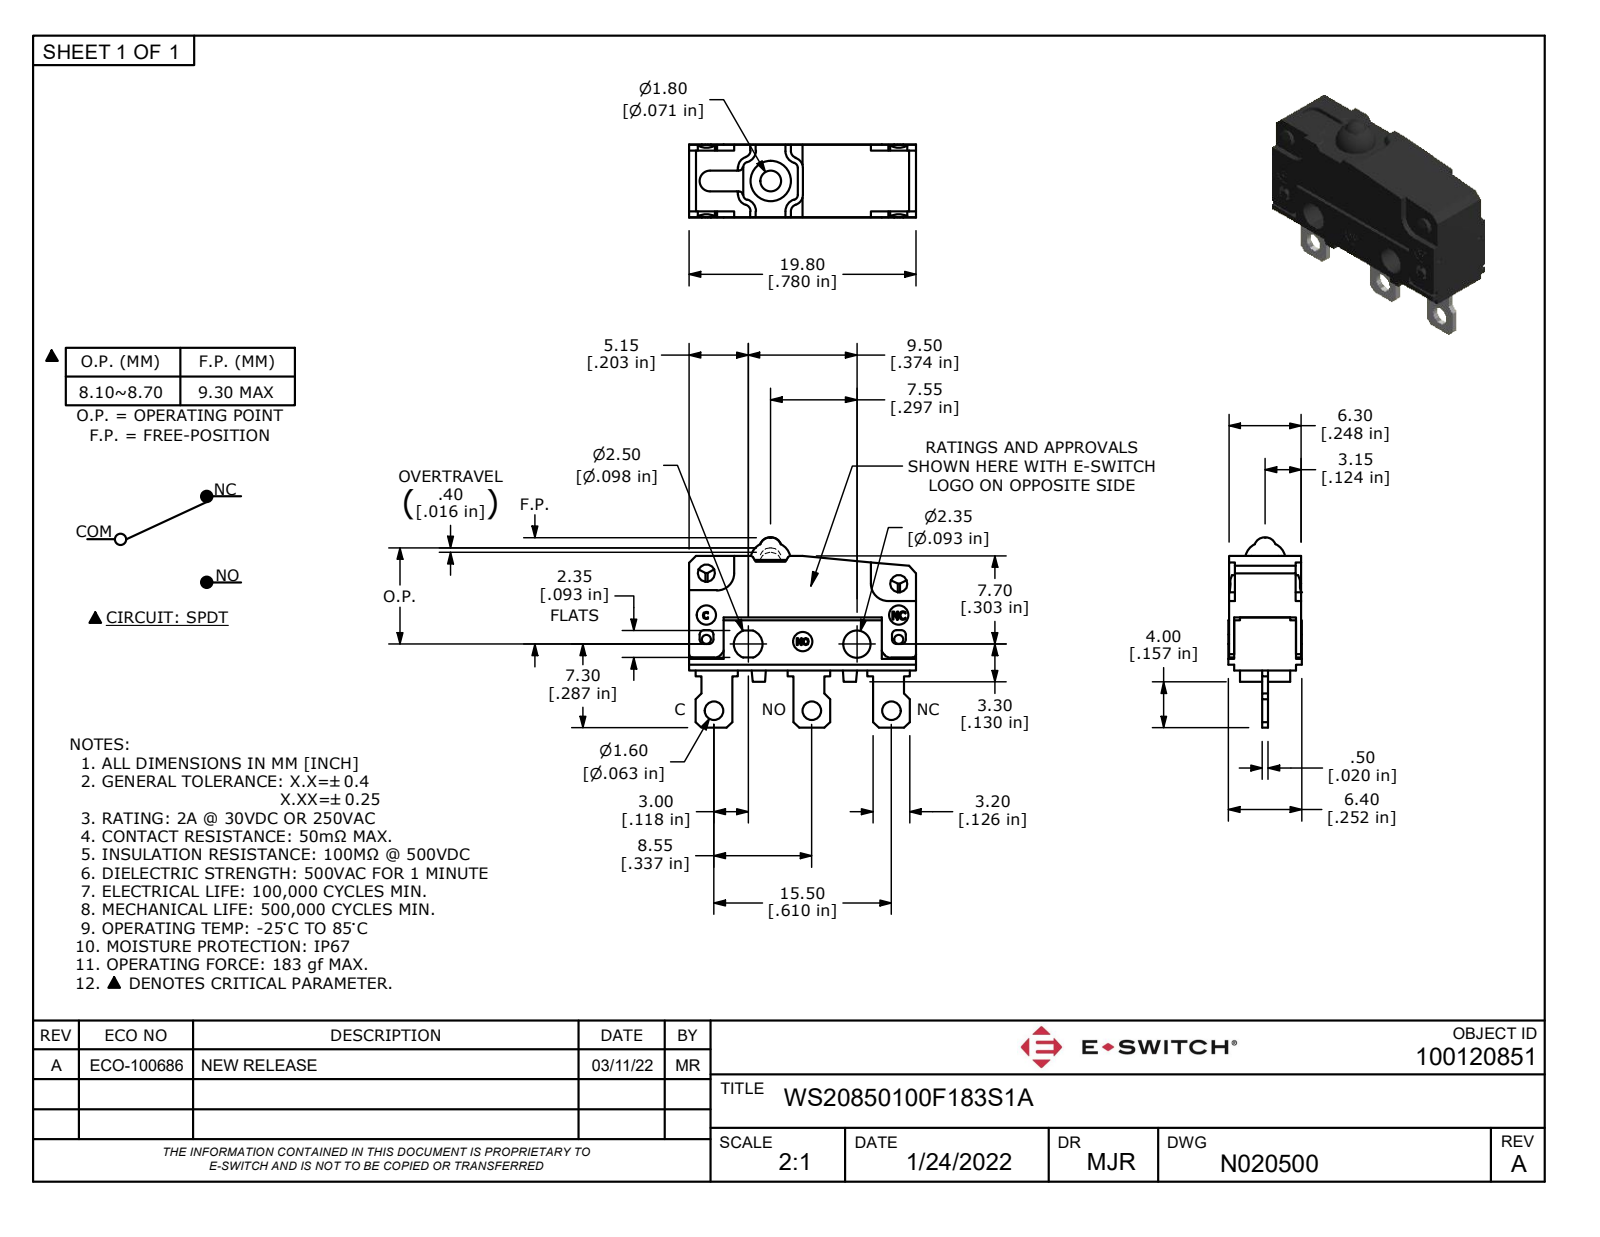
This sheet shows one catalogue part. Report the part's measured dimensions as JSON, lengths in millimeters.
{"part_name": "WS20850100F183S1A", "step_written_by": "Autodesk Inventor 2020 (AUTOMOTIVE_DESIGN)", "units": "millimeters", "bodies": {"solids": 1, "faces": 376, "planar": 237, "cylindrical": 68, "other": 71}, "overall_size": [19.8, 16.6, 6.4], "volume_mm3": 1149, "surface_area_mm2": 1077, "round_holes": [[1.6, 3], [1.7, 3], [2.35, 1]], "round_bosses_or_shafts": [[1.5, 2], [0.8, 2], [3.5, 1]], "partial_cylinders_radius": [[0.3, 10], [0.4, 8], [0.1, 2], [0.8, 2], [1.5, 2], [0.9, 1], [1.25, 1]], "face_to_face_distances": [0.5, 2.9, 2.95, 6.35, 6.3, 3.45, 3.4, 5.85, 19.8, 0.45], "hole_center_spacings": [8.35, 8.71, 9.81, 18.17, 4.44, 4.76, 6.07, 6.53]}
